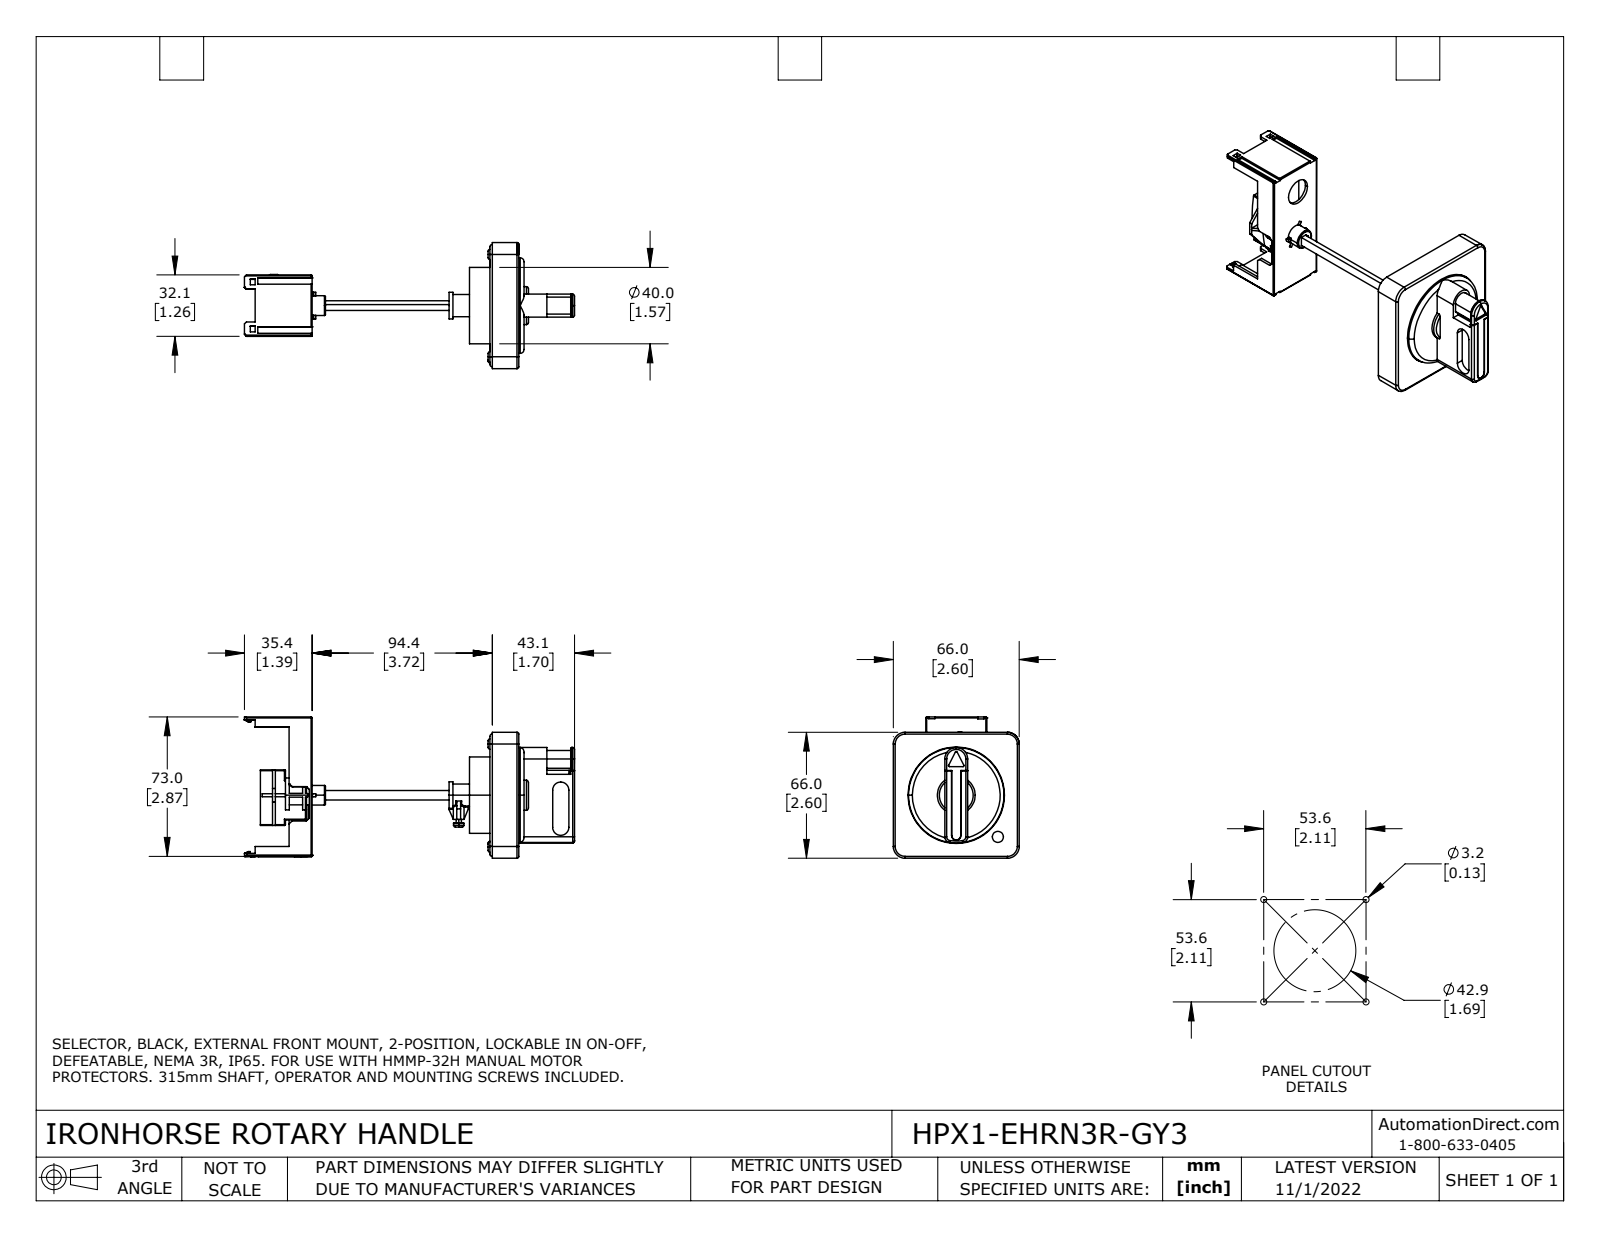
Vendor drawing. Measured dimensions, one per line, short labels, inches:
name: HPX1-EHRN3R-GY3
written by: SolidWorks 2021 (CONFIG_CONTROL_DESIGN)
unit: in
bodies: 4 solids, 807 faces (477 planar, 215 cylindrical, 115 other)
size: 6.808 × 2.914 × 2.598
volume: 6.439 in³; area: 65.83 in²
holes: 2× ⌀0.11, 1× ⌀0.126, 1× ⌀0.228, 1× ⌀0.252, 1× ⌀0.417, 1× ⌀0.551, 1× ⌀1.988
bosses: 6× ⌀0.213, 2× ⌀0.109, 1× ⌀1.969, 1× ⌀1.575, 1× ⌀1.307, 1× ⌀0.709, 1× ⌀0.551, 1× ⌀0.461
rounds: 26× R0.02, 24× R0.008, 10× R0.039, 7× R0.138, 4× R0.052, 4× R0.118, 4× R0.244, 2× R0.01
face distances: 0.059, 1.201, 0.547, 3.717, 4.264, 1.398, 3.776, 4.323, 0.058, 2.598
hole spacings: 0.267, 0.772, 1.03, 1.214, 1.842, 2.042
